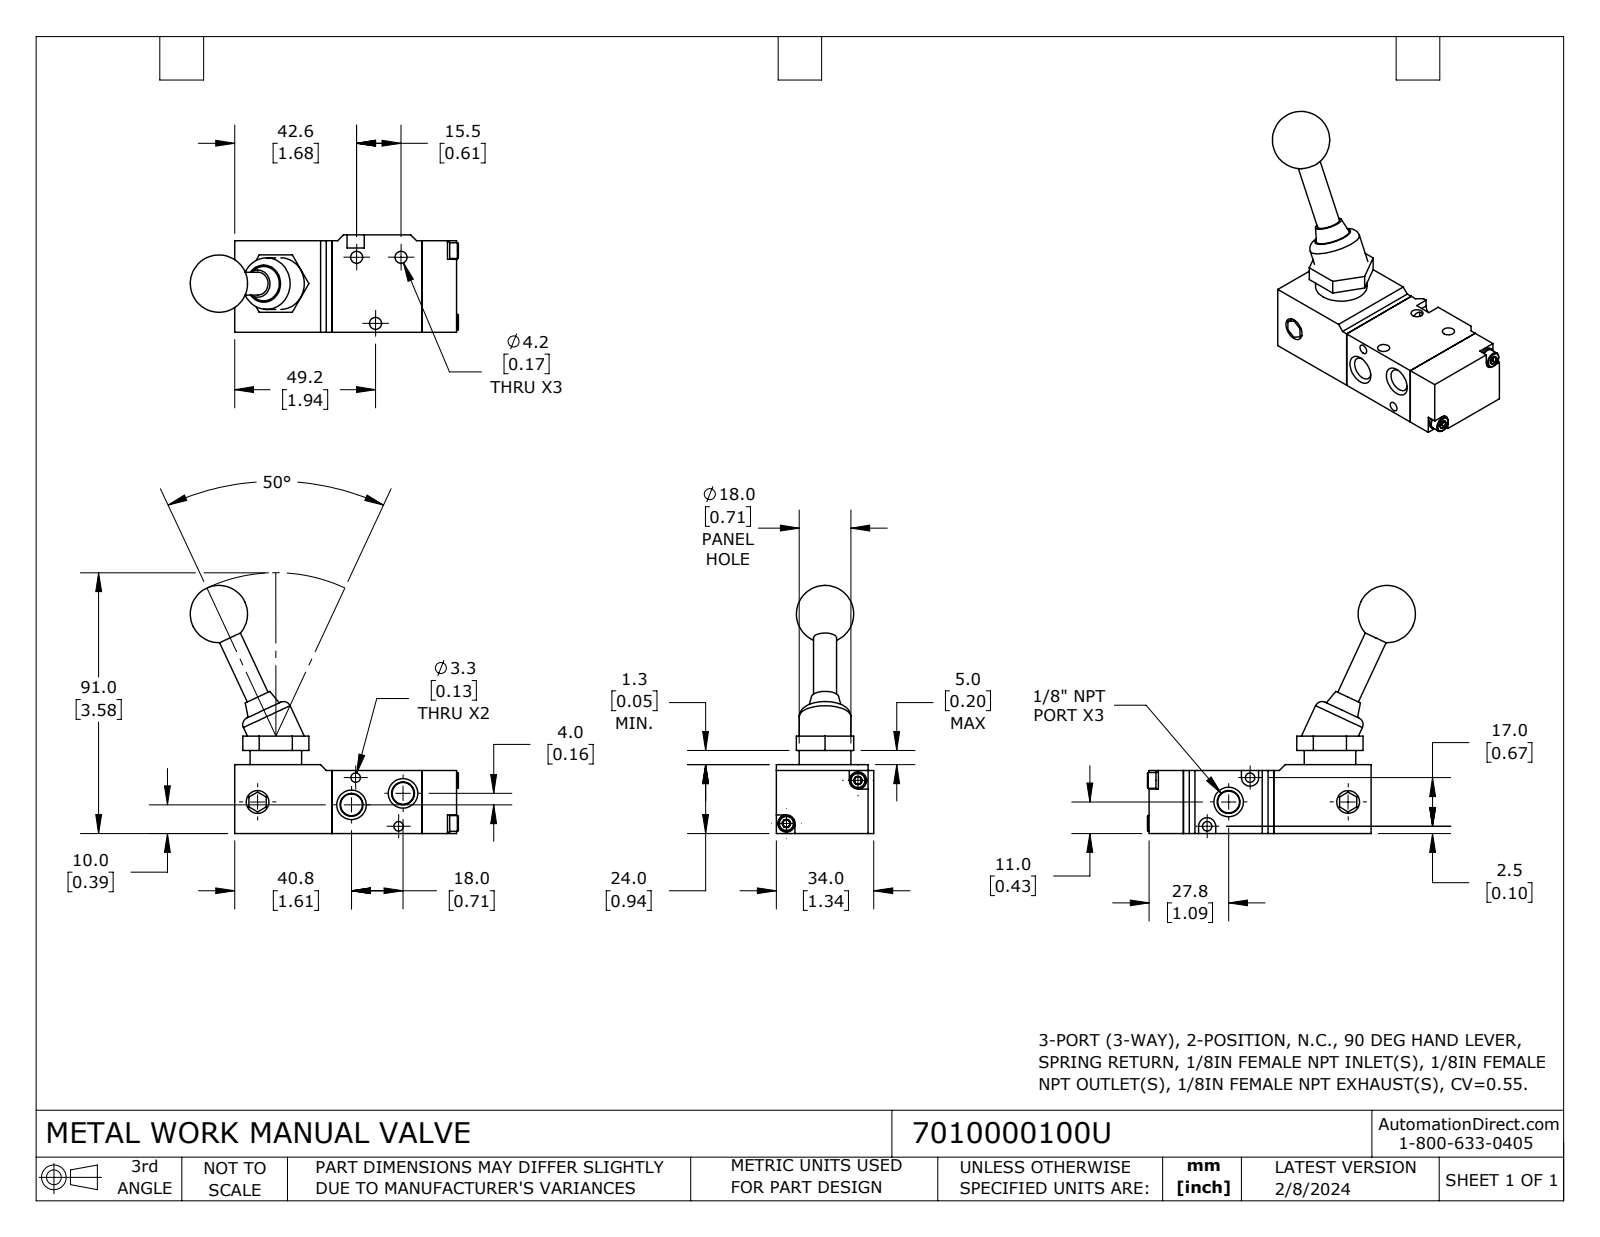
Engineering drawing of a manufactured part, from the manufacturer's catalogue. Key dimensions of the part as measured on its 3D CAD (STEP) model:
Part name (STEP PRODUCT): 7010000100U
STEP written by: SolidWorks 2023 (CONFIG_CONTROL_DESIGN)
Units: inches
Bodies: 8 solids, 190 faces (100 planar, 44 cylindrical, 46 other)
Overall size (bounding box): 3.685 × 3.409 × 1.339
Volume: 4.096 in³ · Surface area: 30.32 in²
Round holes (diameter × count): ⌀0.165 ×3, ⌀0.118 ×2, ⌀0.13 ×2, ⌀0.313 ×1
Round bosses / shafts (diameter × count): ⌀0.709 ×2, ⌀0.236 ×2, ⌀0.217 ×2, ⌀0.315 ×1
Partial cylindrical surfaces — rounded edges, fillets, slot ends (radius × count): R0.118 ×2
Main face-to-face distances: 1.339, 0.866, 1.24, 1.26, 0.079, 0.472, 2.579, 0.945, 1.713, 3.051
Hole centre spacings: 0.61, 0.893, 0.946, 0.975, 1.148, 1.389, 1.968
